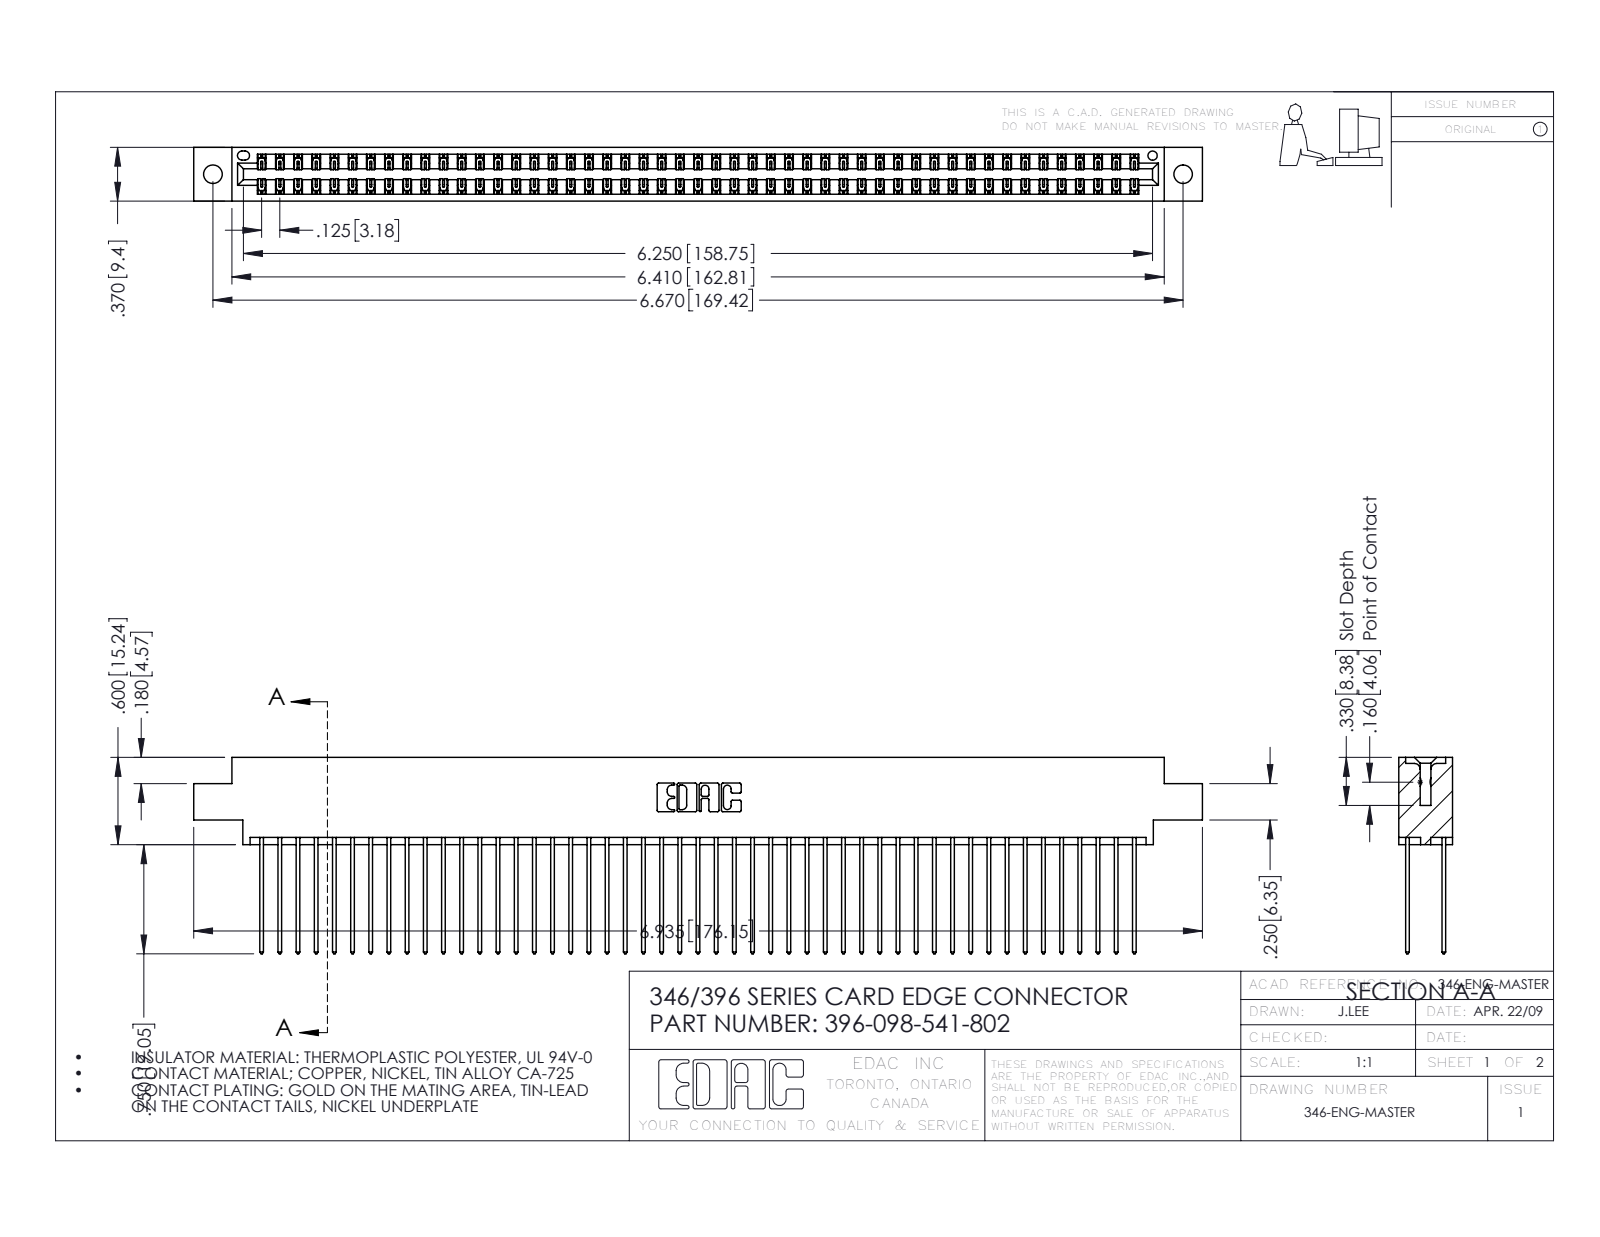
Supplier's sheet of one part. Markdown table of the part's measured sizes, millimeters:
| quantity | value |
| --- | --- |
| part name | 396-098-541-802; 345-292-001_345-293-141; 346 Part_0.170 Offset - 0.128 Dia |
| STEP written by | SolidWorks 2016 (CONFIG_CONTROL_DESIGN) |
| units | millimeters |
| bodies | 99 solids, 5222 faces (3510 planar, 1712 cylindrical, 0 other) |
| overall size | 176.1 × 34.3 × 9.4 |
| volume | 17 600 mm³ |
| surface area | 26 910 mm² |
| round holes (diameter × count) | 3.3 × 2, 1.6 × 1 |
| partial cylindrical surfaces (radius × count) | 0.2 × 147, 0.3 × 98, 0.3 × 22, 0.2 × 6, 0.8 × 6, 0.7 × 3, 0.4 × 2, 0.6 × 2 |
| main face-to-face distances | 1.2, 8.2, 6.4, 1.8, 7.6, 0.6, 9.4, 7, 5.7, 3.8 |
| hole center spacings | 6.2, 164.1, 169.4 |
